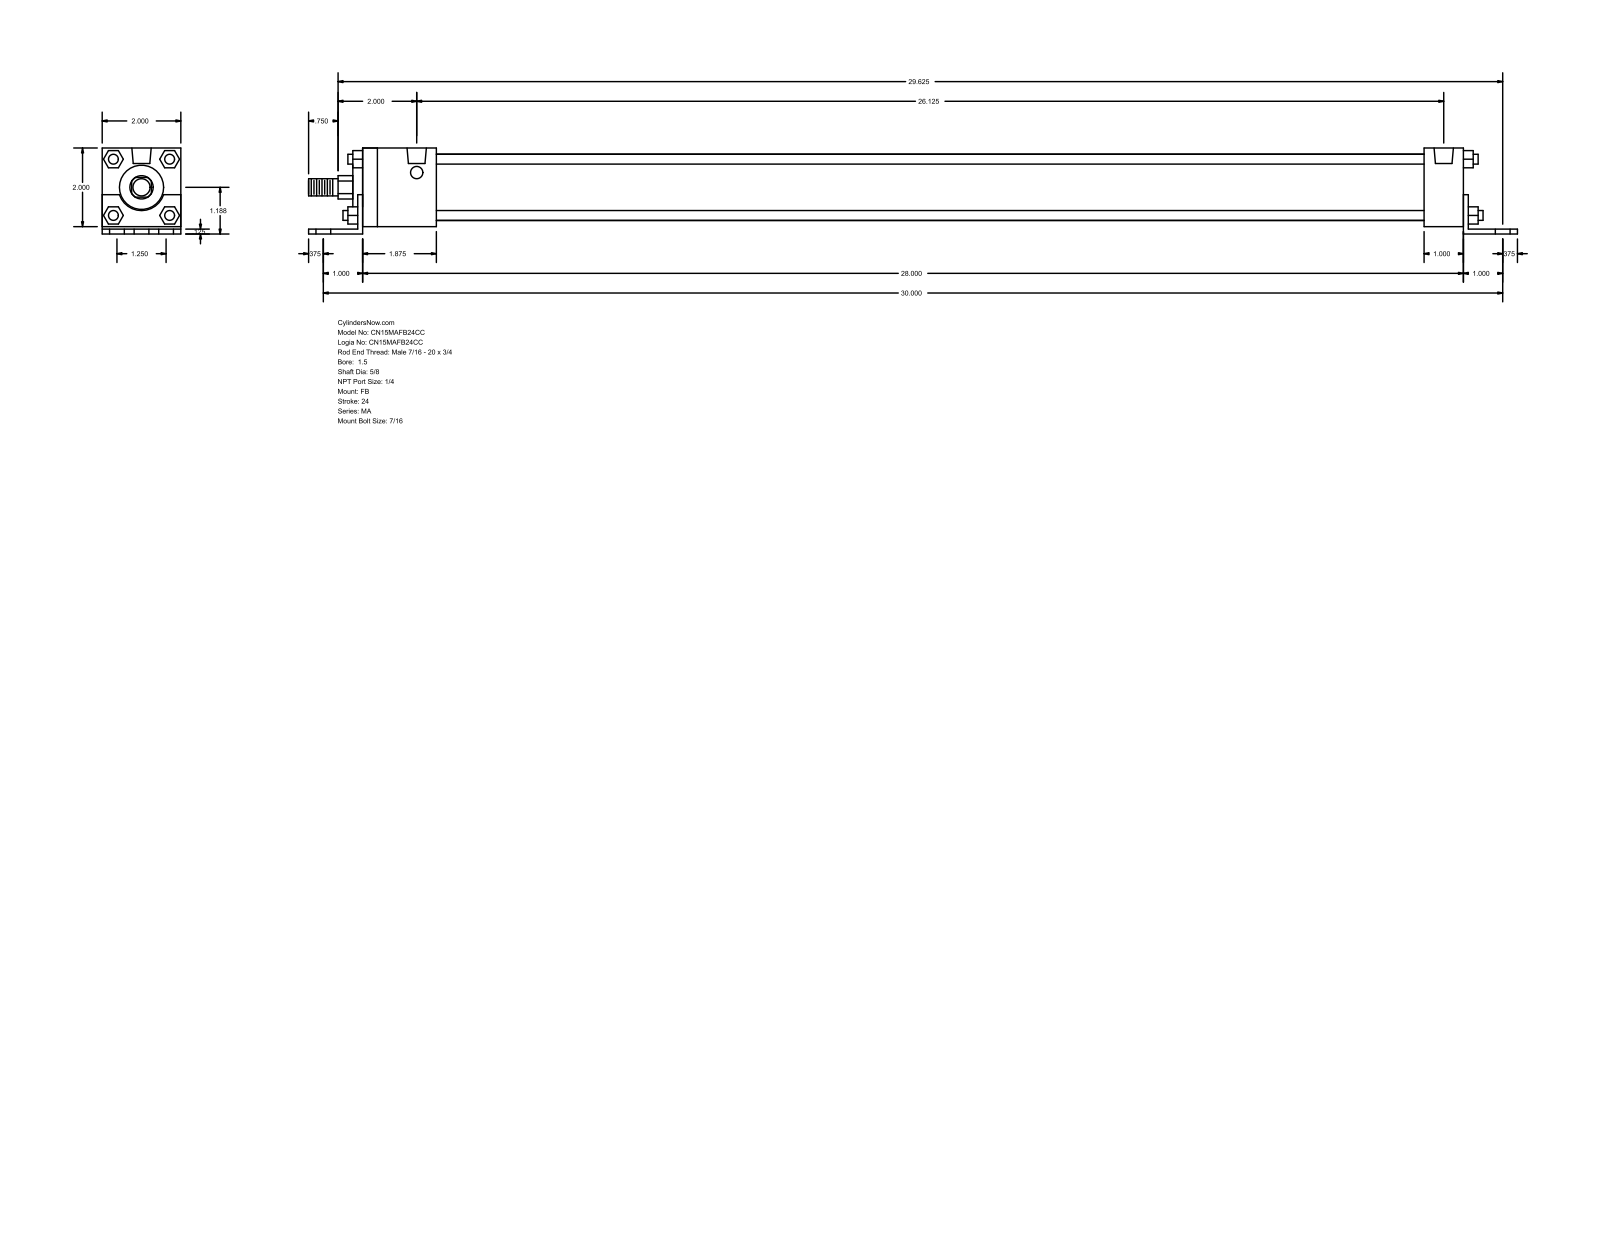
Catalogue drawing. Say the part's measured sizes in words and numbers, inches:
The part is named "MA_FB__0150_0.625". Its 3-D file was written by "GSSL Pune (CONFIG_CONTROL_DESIGN)". It is 0 solids with 140 faces: 105 planar, 35 cylindrical and 0 other. Overall it measures 30.75 by 2.187 by 2 inches. Round holes: 6 of diameter 0.437, 4 of diameter 0.313, 2 of diameter 0.492. Round bosses or shafts: 4 of diameter 0.25, 1 of diameter 1.69, 1 of diameter 1.125, 1 of diameter 0.625, 1 of diameter 0.437. Partial cylindrical surfaces (rounded edges, fillets, slot ends): 1 of radius 0.297, 1 of radius 0.593. The main face-to-face distances are 2, 0.125, 0.187, 2.187, 0.063, 2.063, 1.125, 28.25, 28.375, 0.25. The hole center spacings are 0.625, 30.007, 30, 1.25, 1.625, 2.456, 26.125, 27.632.
